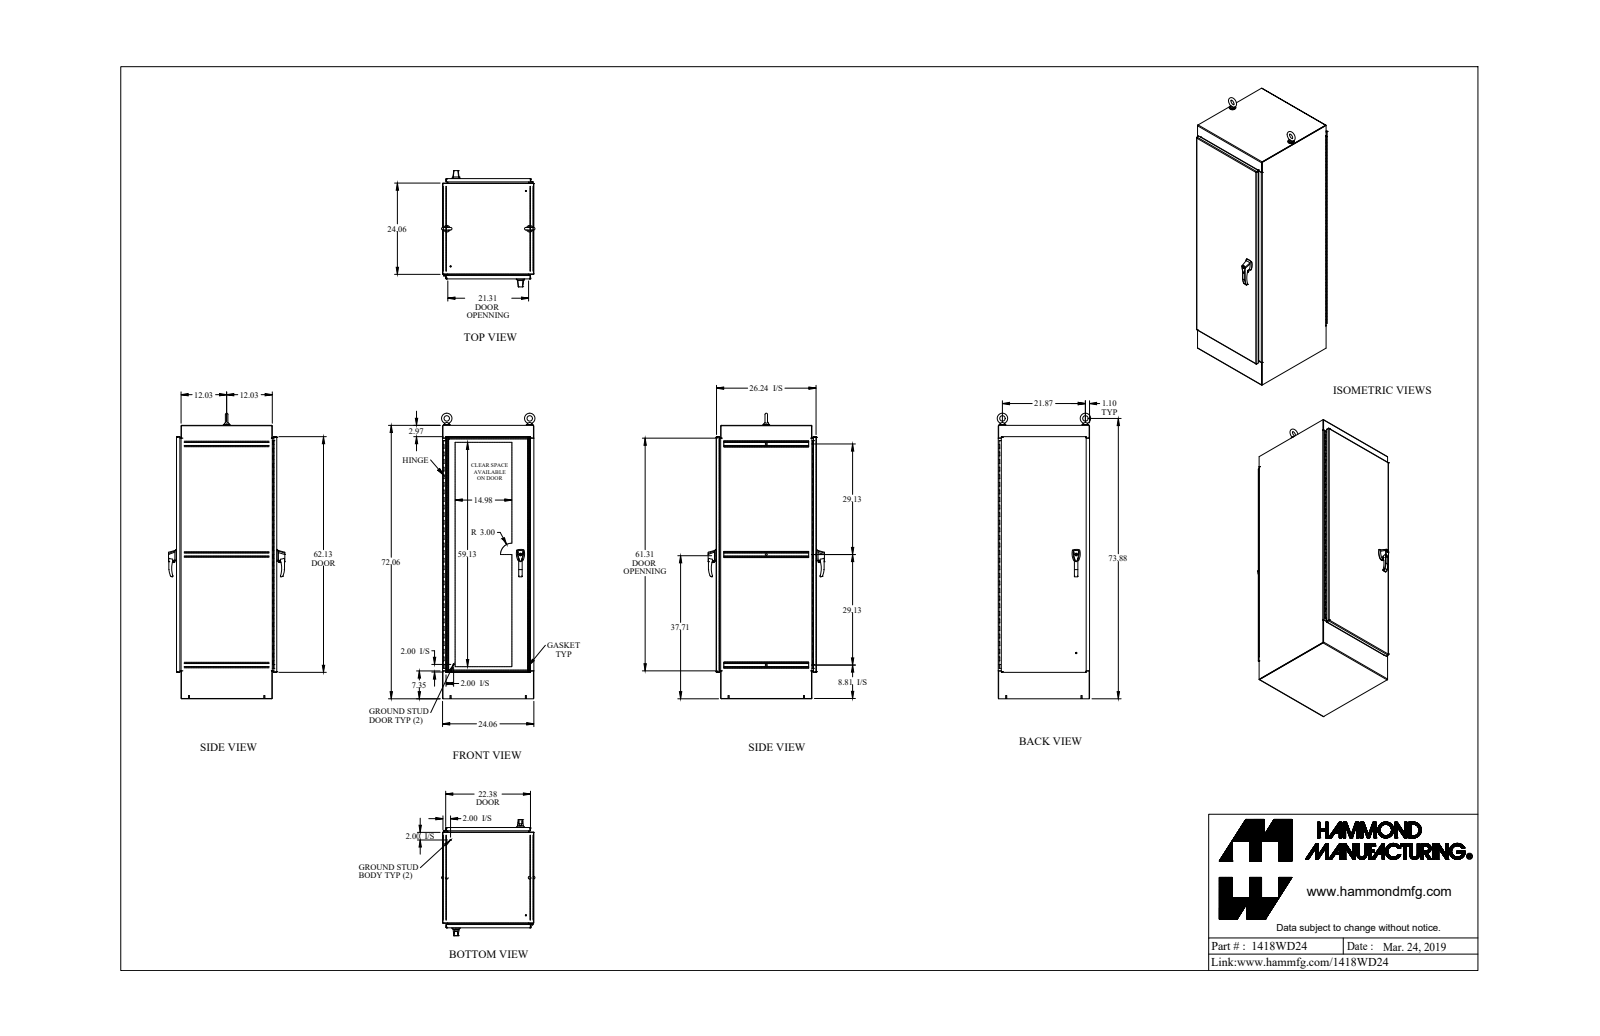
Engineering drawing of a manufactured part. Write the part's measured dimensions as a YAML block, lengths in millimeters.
part_name: "1418WD24"
step_written_by: "SolidWorks 2019 (AUTOMOTIVE_DESIGN)"
units: millimeters
bodies: {solids: 83, faces: 2484, planar: 1358, cylindrical: 886, other: 240}
overall_size: [1923.1, 778.9, 638]
volume: 16570000
surface_area: 13770000
round_holes:
  - {diameter: 7.7, count: 20}
  - {diameter: 6.4, count: 4}
  - {diameter: 6.5, count: 4}
  - {diameter: 7.1, count: 4}
  - {diameter: 7.1, count: 4}
  - {diameter: 8, count: 4}
  - {diameter: 9.9, count: 4}
  - {diameter: 10.5, count: 4}
  - {diameter: 12.7, count: 3}
  - {diameter: 2.8, count: 2}
  - {diameter: 4.4, count: 2}
  - {diameter: 5.9, count: 2}
round_bosses_or_shafts:
  - {diameter: 7.1, count: 8}
  - {diameter: 25.4, count: 4}
  - {diameter: 19.1, count: 4}
  - {diameter: 16, count: 4}
  - {diameter: 11.2, count: 4}
  - {diameter: 9.4, count: 4}
  - {diameter: 6.4, count: 4}
  - {diameter: 15.9, count: 3}
partial_cylinders:
  - {radius: 3.2, count: 44}
  - {radius: 1.1, count: 42}
  - {radius: 3.5, count: 36}
  - {radius: 0.4, count: 32}
  - {radius: 1.2, count: 24}
  - {radius: 3.6, count: 24}
  - {radius: 1.5, count: 16}
  - {radius: 8.1, count: 14}
face_to_face_distances: [2.4, 608.7, 669, 606.3, 611.1, 638.9, 30.1, 666.6, 671.4, 1827.9]
hole_center_spacings: [152.4, 587.4, 304.8, 643.9, 457.2, 728.5, 609.6, 832.7]
